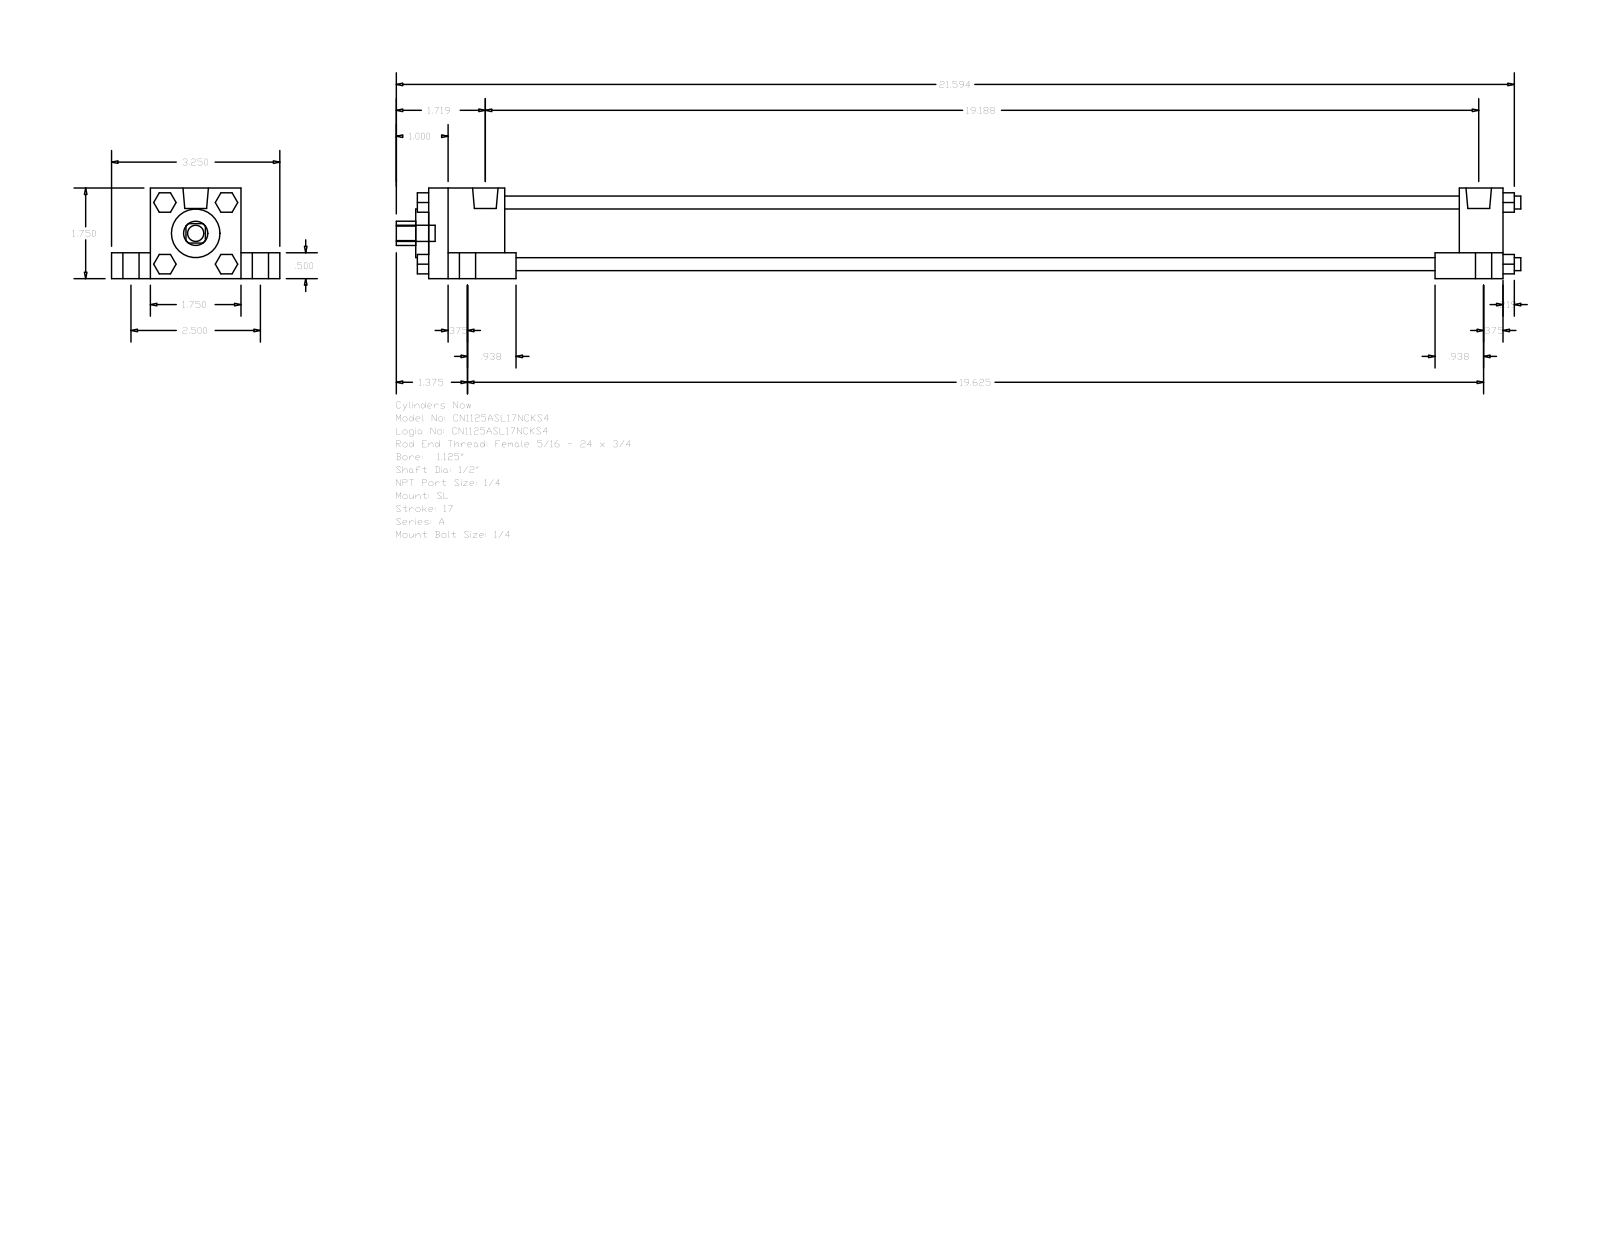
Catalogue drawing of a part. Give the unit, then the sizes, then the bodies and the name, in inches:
Units: inches
Overall size (bounding box): 21.719 × 3.25 × 1.75
Round holes (diameter × count): ⌀0.5 ×1, ⌀0.937 ×1, ⌀1.255 ×1
Round bosses / shafts (diameter × count): ⌀0.313 ×5, ⌀0.563 ×4, ⌀0.25 ×4, ⌀0.219 ×4, ⌀0.492 ×2
Partial cylindrical surfaces — rounded edges, fillets, slot ends (radius × count): R0.234 ×1
Main face-to-face distances: 1.75, 1.25, 0.5, 0.75, 2.5, 19.281, 20.75, 19.906, 0.844, 1.469
Bodies: 0 solids, 150 faces (114 planar, 36 cylindrical, 0 other)
Part name (STEP PRODUCT): A_SL__0112_0.5
STEP written by: GSSL Pune (CONFIG_CONTROL_DESIGN)
